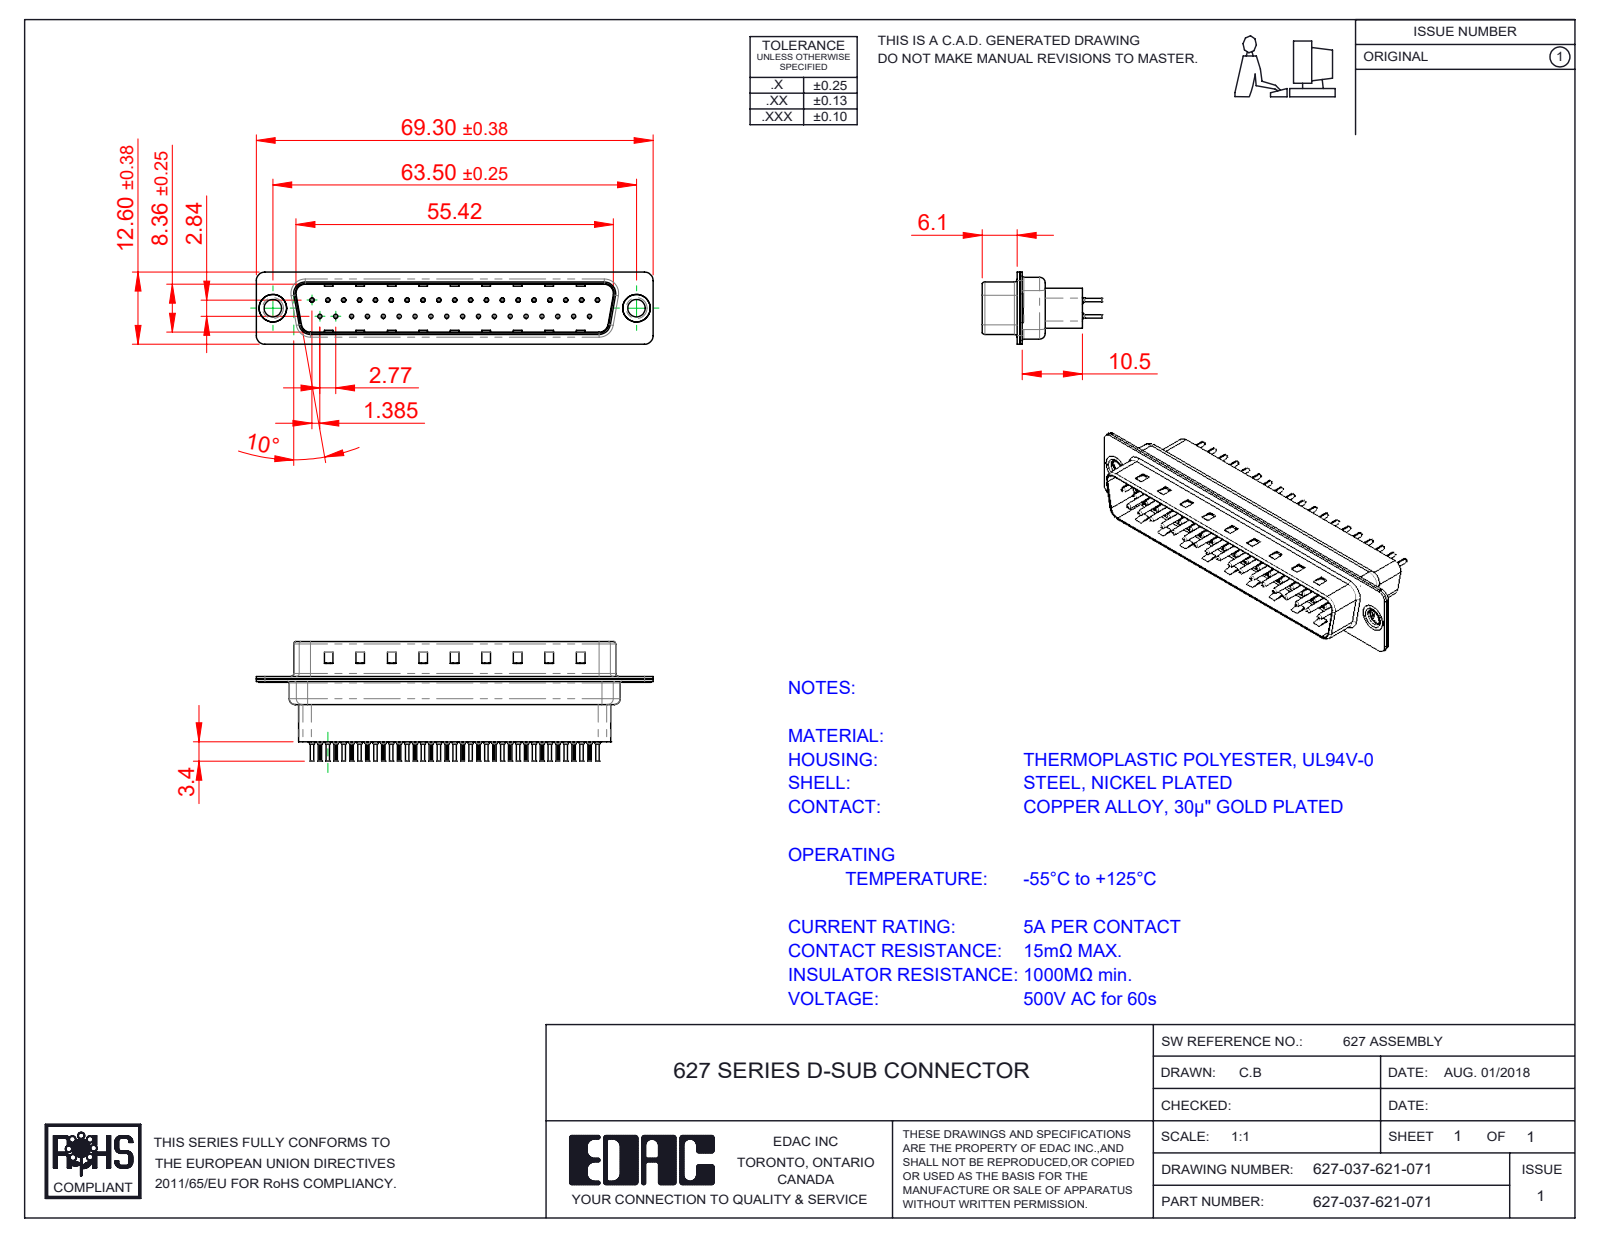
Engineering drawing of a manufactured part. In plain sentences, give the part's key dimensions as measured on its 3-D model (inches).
The part is named "627 Thru Hole Rivet; 627 Housing_37 HP; 627-037-621-071; 627 Contact Row 1_21H (+3 more)". Its 3-D file was written by "SolidWorks 2020 (CONFIG_CONTROL_DESIGN)". It is 42 solids with 4012 faces: 1091 planar, 1494 cylindrical and 1427 other. Overall it measures 2.728 by 0.819 by 0.496 inches. Its volume is 0.319 cubic inches and its surface area 20.79 square inches. Round holes: 37 of diameter 0.008, 37 of diameter 0.014, 37 of diameter 0.043, 37 of diameter 0.063, 2 of diameter 0.12, 2 of diameter 0.157, 2 of diameter 0.189. Round bosses or shafts: 37 of diameter 0.079, 37 of diameter 0.059, 37 of diameter 0.03, 37 of diameter 0.024, 2 of diameter 0.197, 2 of diameter 0.193, 2 of diameter 0.14. Partial cylindrical surfaces (rounded edges, fillets, slot ends): 74 of radius 0.004, 16 of radius 0.059, 12 of radius 0.079, 8 of radius 0.02, 8 of radius 0.063, 4 of radius 0.01, 4 of radius 0.024, 4 of radius 0.026. The main face-to-face distances are 0.016, 0.032, 0.377, 0.027, 0.302, 0.018, 0.059, 0.043, 0.318, 0.345. The hole center spacings are 0.124, 0.109, 0.218, 0.327, 0.198, 0.398, 0.436, 0.503.
